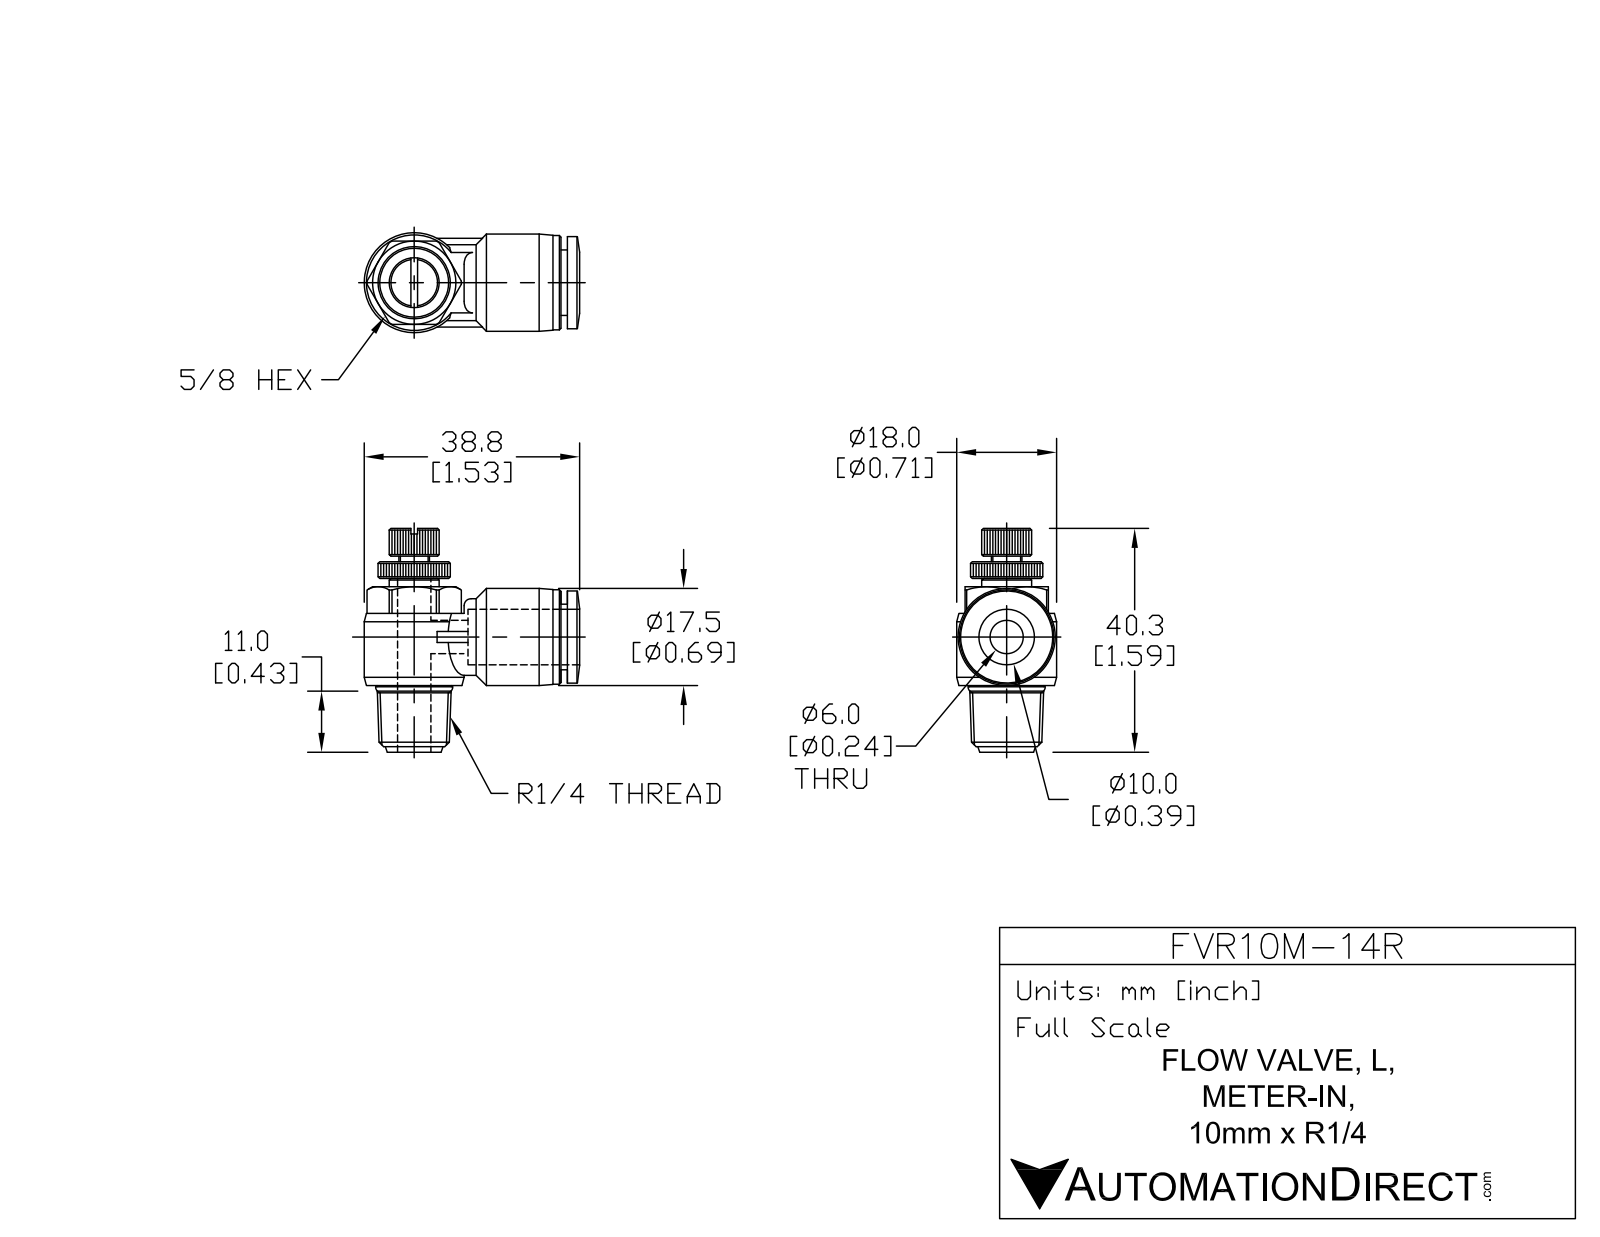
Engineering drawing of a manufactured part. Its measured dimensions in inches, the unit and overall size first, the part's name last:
Units: inches
Overall size (bounding box): 1.835 × 1.528 × 0.709
Round holes (diameter × count): ⌀0.177 ×2, ⌀0.406 ×1
Round bosses / shafts (diameter × count): ⌀0.709 ×1, ⌀0.689 ×1, ⌀0.669 ×1, ⌀0.654 ×1, ⌀0.543 ×1, ⌀0.528 ×1, ⌀0.465 ×1, ⌀0.354 ×1
Partial cylindrical surfaces — rounded edges, fillets, slot ends (radius × count): R0.256 ×1, R0.335 ×1
Main face-to-face distances: 0.591, 0.045, 0.177, 0.701, 0.878, 1.173, 0.659, 0.705, 0.76, 0.059
Volume: 0.556 in³ · Surface area: 7.964 in²
Bodies: 1 solid, 422 faces (188 planar, 110 cylindrical, 124 other)
Part name (STEP PRODUCT): FVR10M-14R
STEP written by: SolidWorks 2015 (AUTOMOTIVE_DESIGN)
